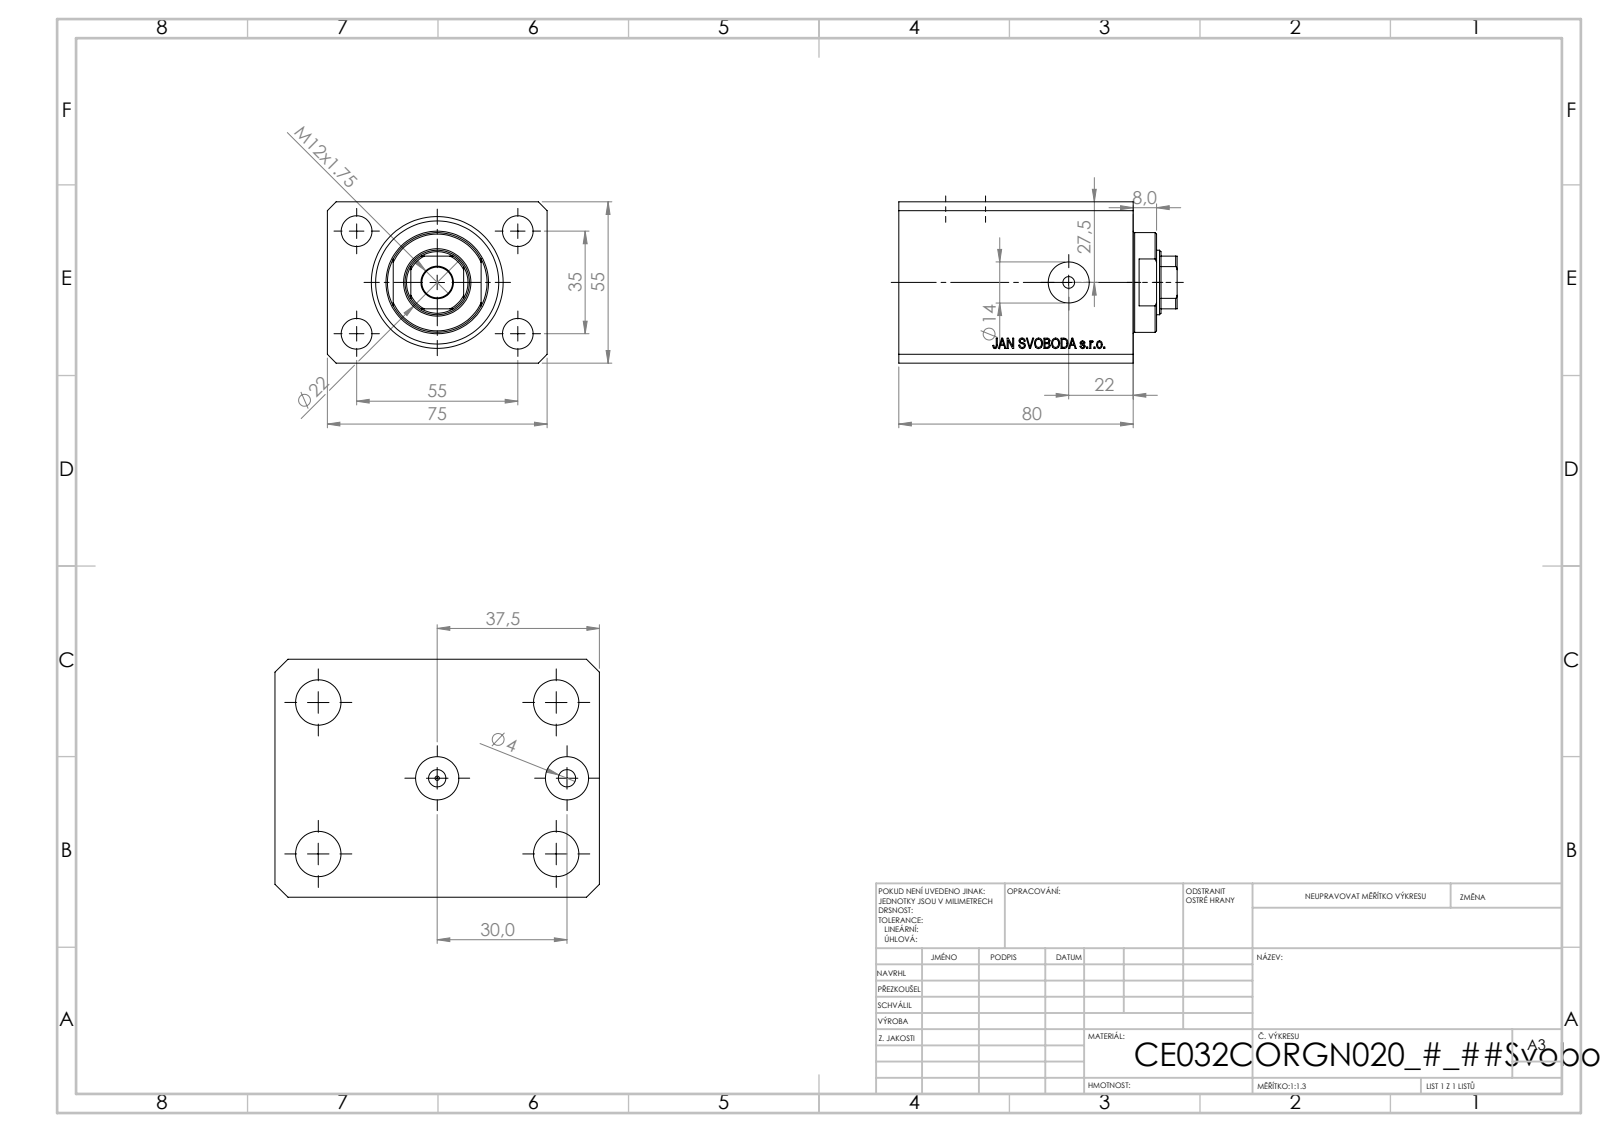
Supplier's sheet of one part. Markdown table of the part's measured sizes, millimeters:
| quantity | value |
| --- | --- |
| part name | V250CE_C_Body; V250CE_C_VCP; V250CE_VC_C |
| STEP written by | SolidWorks 2019 (CONFIG_CONTROL_DESIGN) |
| units | millimeters |
| bodies | 3 solids, 872 faces (428 planar, 50 cylindrical, 394 other) |
| overall size | 95 × 75 × 55 |
| volume | 296 169 mm³ |
| surface area | 64 654 mm² |
| round holes (diameter × count) | 10.5 × 5, 4 × 4, 10 × 2, 14 × 2, 1.25 × 1, 22 × 1, 32 × 1, 45 × 1 |
| round bosses / shafts (diameter × count) | 34 × 1 |
| partial cylindrical surfaces (radius × count) | 10.5 × 1 |
| main face-to-face distances | 55, 75, 80, 15, 65, 9.9, 55.1, 70.1, 87.66, 8 |
| hole center spacings | 32.6, 17.68, 35, 55, 60.1, 65.19, 30, 36 |
